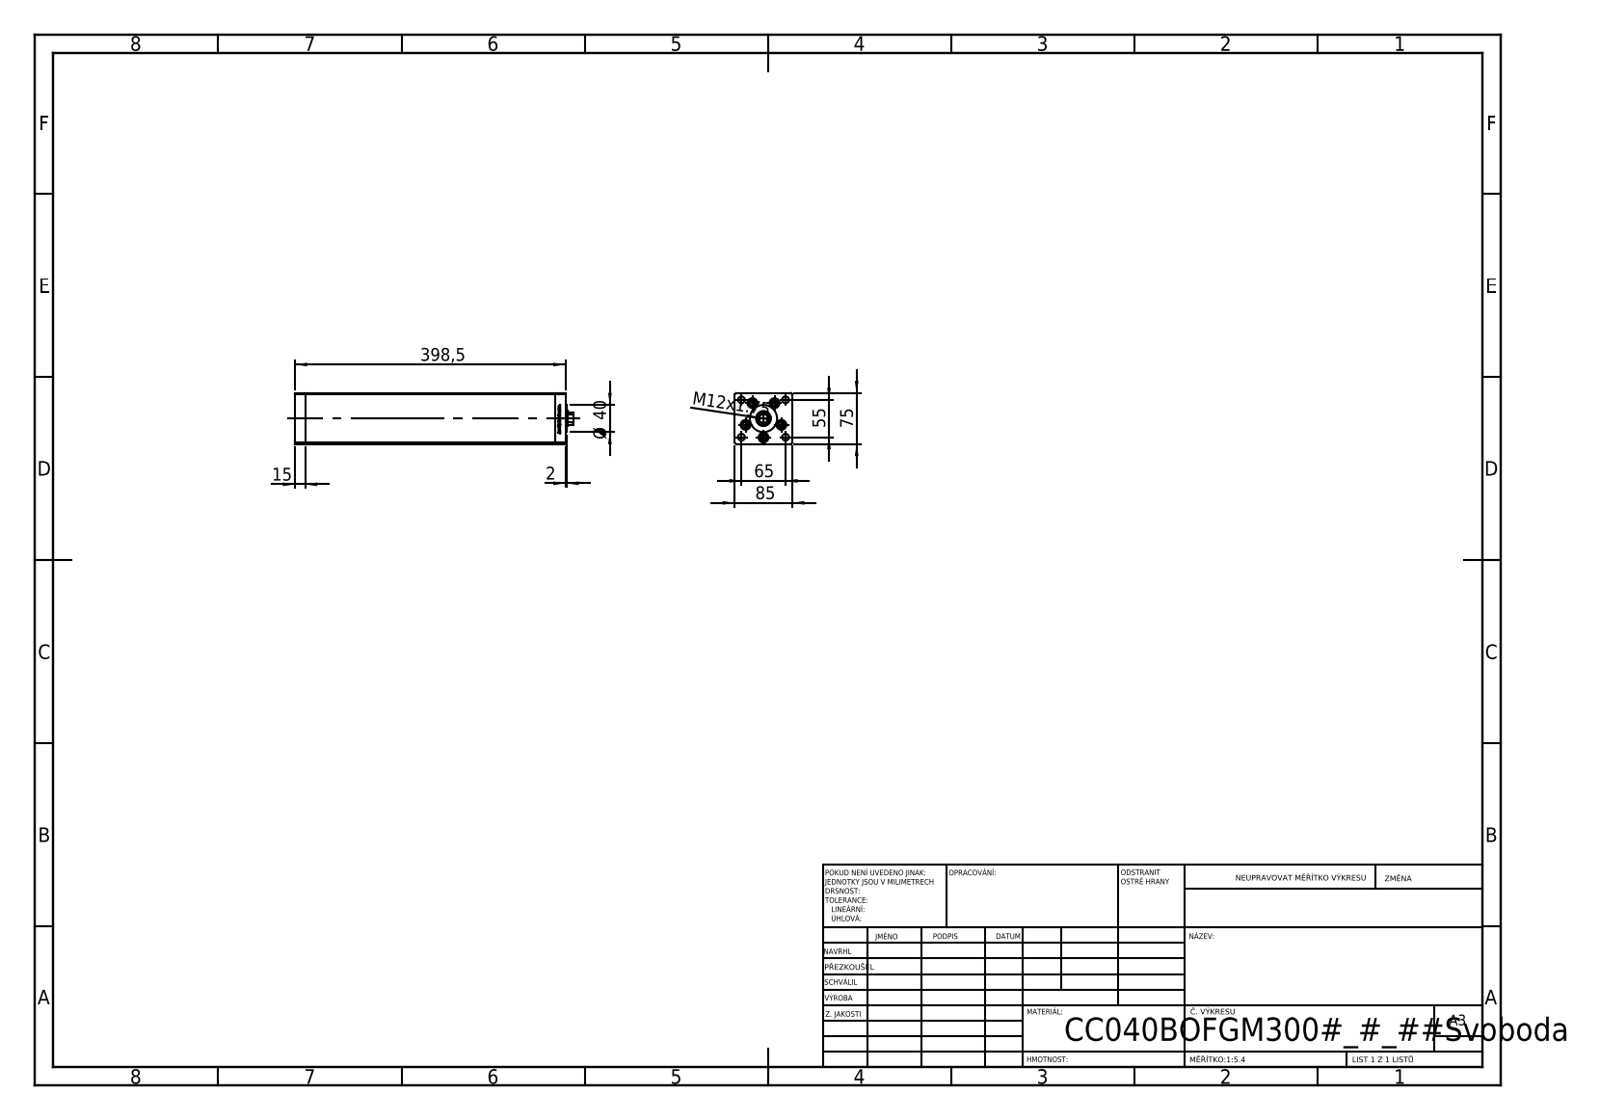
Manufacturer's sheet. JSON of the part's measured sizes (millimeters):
{"part_name": "V220C_B MIDDLE; V220C_VC_B; V220C BACK_B; V220C_FRONT_B (+1 more)", "step_written_by": "SolidWorks 2019 (CONFIG_CONTROL_DESIGN)", "units": "millimeters", "bodies": {"solids": 14, "faces": 1173, "planar": 460, "cylindrical": 139, "other": 574}, "overall_size": [410, 85, 75], "volume_mm3": 2181000, "surface_area_mm2": 276781, "round_holes": [[11, 5], [14.5, 5], [10, 4], [13.5, 1], [22, 1]], "round_bosses_or_shafts": [[8, 5], [40, 1]], "partial_cylinders_radius": [[0.93, 2], [10.5, 1]], "face_to_face_distances": [85, 75, 15, 368.5, 383.5, 64.5, 10.5, 31.25, 53.75, 68.5], "hole_center_spacings": [28, 42.57, 16.86, 19.17, 32.33, 32.5, 33.63, 37.33]}
